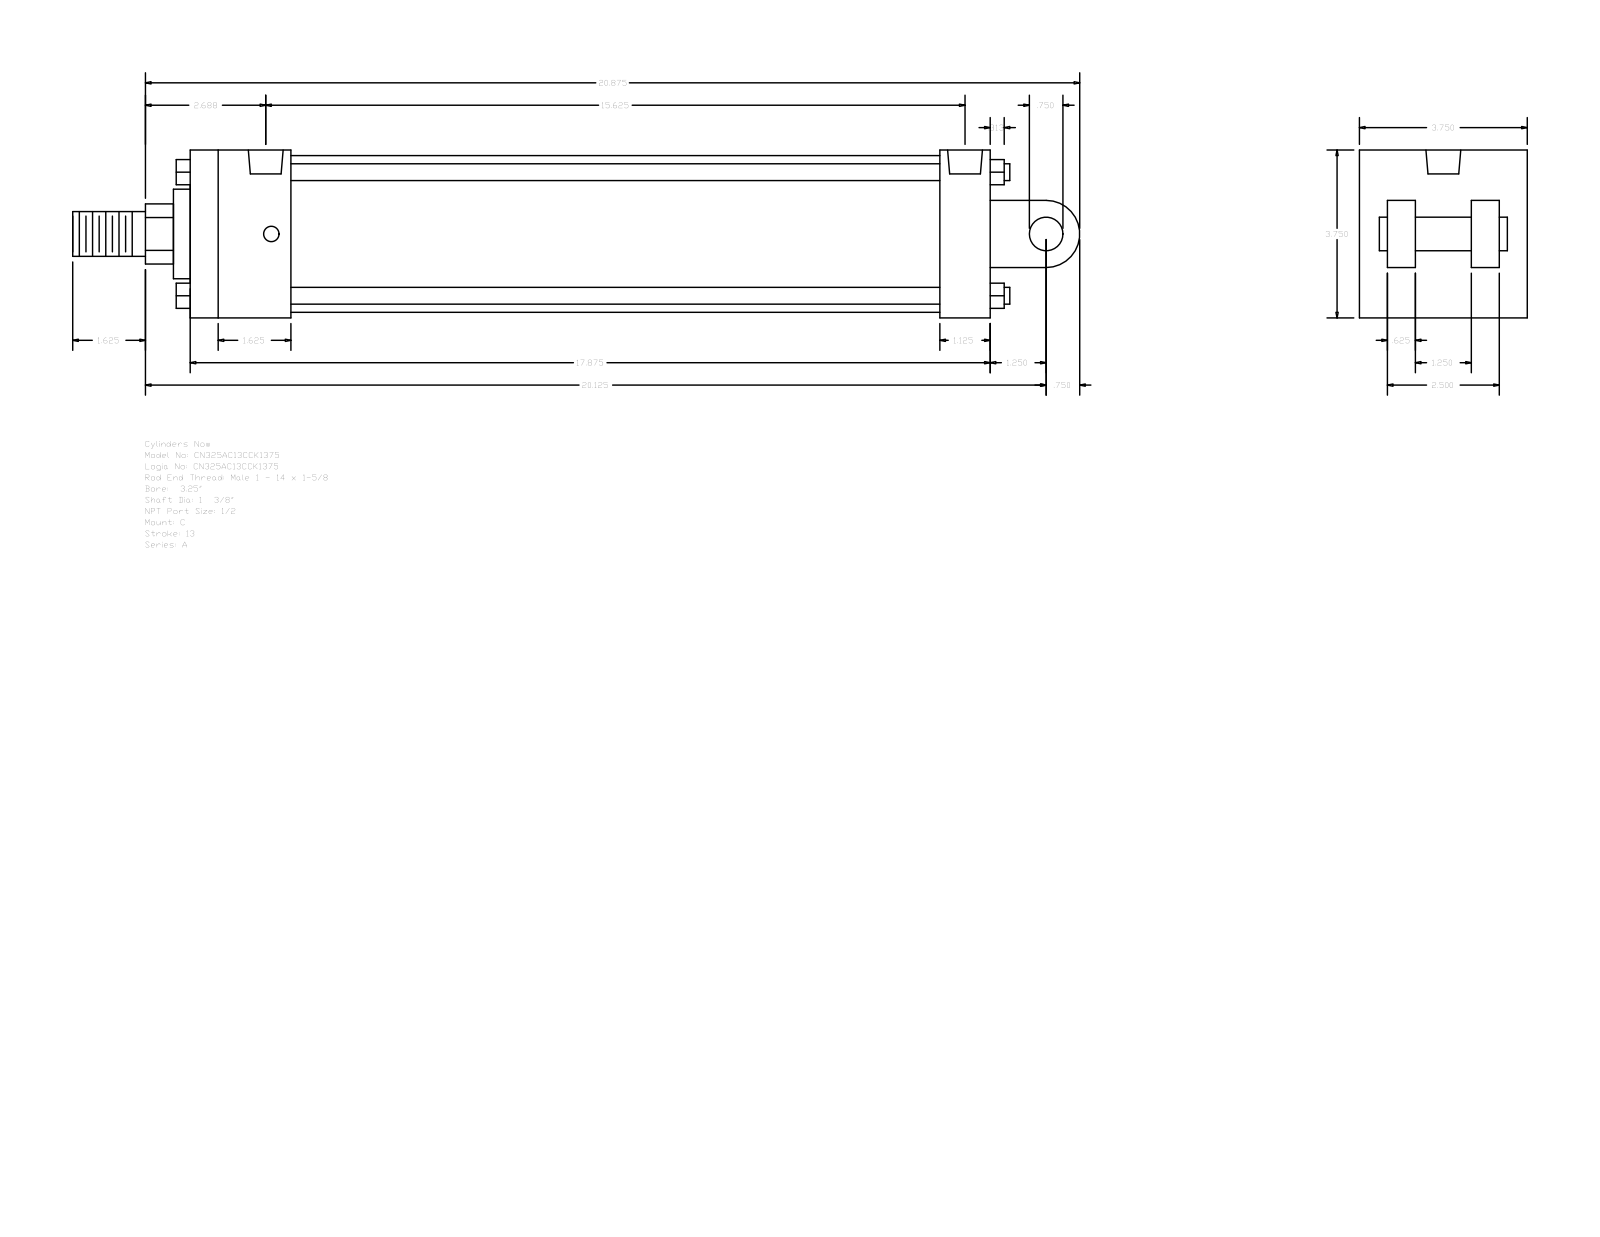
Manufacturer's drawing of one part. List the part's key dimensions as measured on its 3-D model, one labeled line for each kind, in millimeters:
Part name (STEP PRODUCT): A_C__0325_1.375
STEP written by: GSSL Pune (CONFIG_CONTROL_DESIGN)
Units: millimetres
Bodies: 0 solids, 135 faces (102 planar, 33 cylindrical, 0 other)
Overall size (bounding box): 571.5 × 95.25 × 95.25
Round holes (diameter × count): ⌀8.73 ×4, ⌀19.77 ×2
Round bosses / shafts (diameter × count): ⌀9.53 ×4, ⌀88.9 ×1, ⌀50.8 ×1, ⌀34.92 ×1, ⌀25.4 ×1, ⌀19.05 ×1
Partial cylindrical surfaces — rounded edges, fillets, slot ends (radius × count): R17.06 ×1, R19.05 ×1
Main face-to-face distances: 95.24, 454.03, 15.87, 63.5, 66.67, 57.15, 28.58, 79.37, 31.74, 47.63
Hole centre spacings: 3.18, 390.52, 393.7, 396.88
